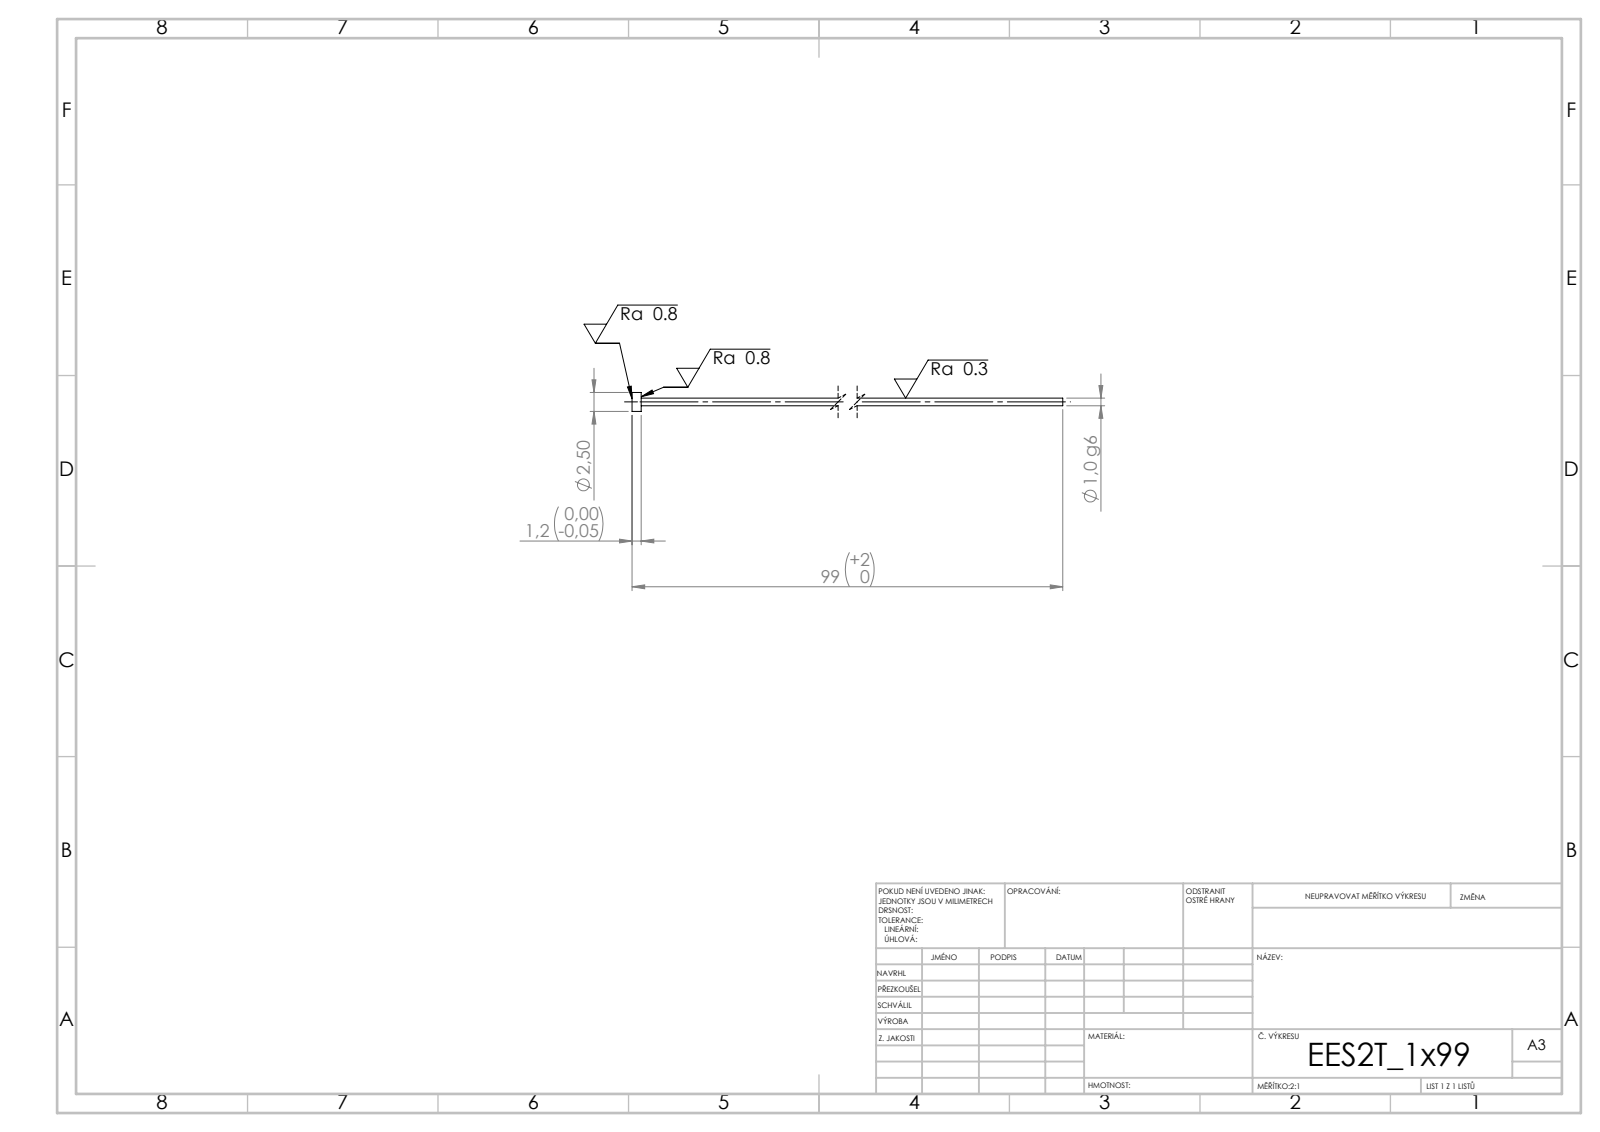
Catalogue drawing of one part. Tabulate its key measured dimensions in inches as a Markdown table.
| quantity | value |
| --- | --- |
| STEP written by | SolidWorks 2019 (CONFIG_CONTROL_DESIGN) |
| units | inches |
| bodies | 1 solid, 7 faces (3 planar, 4 cylindrical, 0 other) |
| overall size | 3.898 × 0.098 × 0.098 |
| volume | 0.005 in³ |
| surface area | 0.505 in² |
| round bosses / shafts (diameter × count) | 0.098 × 1, 0.039 × 1 |
| main face-to-face distances | 0.047, 3.898, 3.85 |
